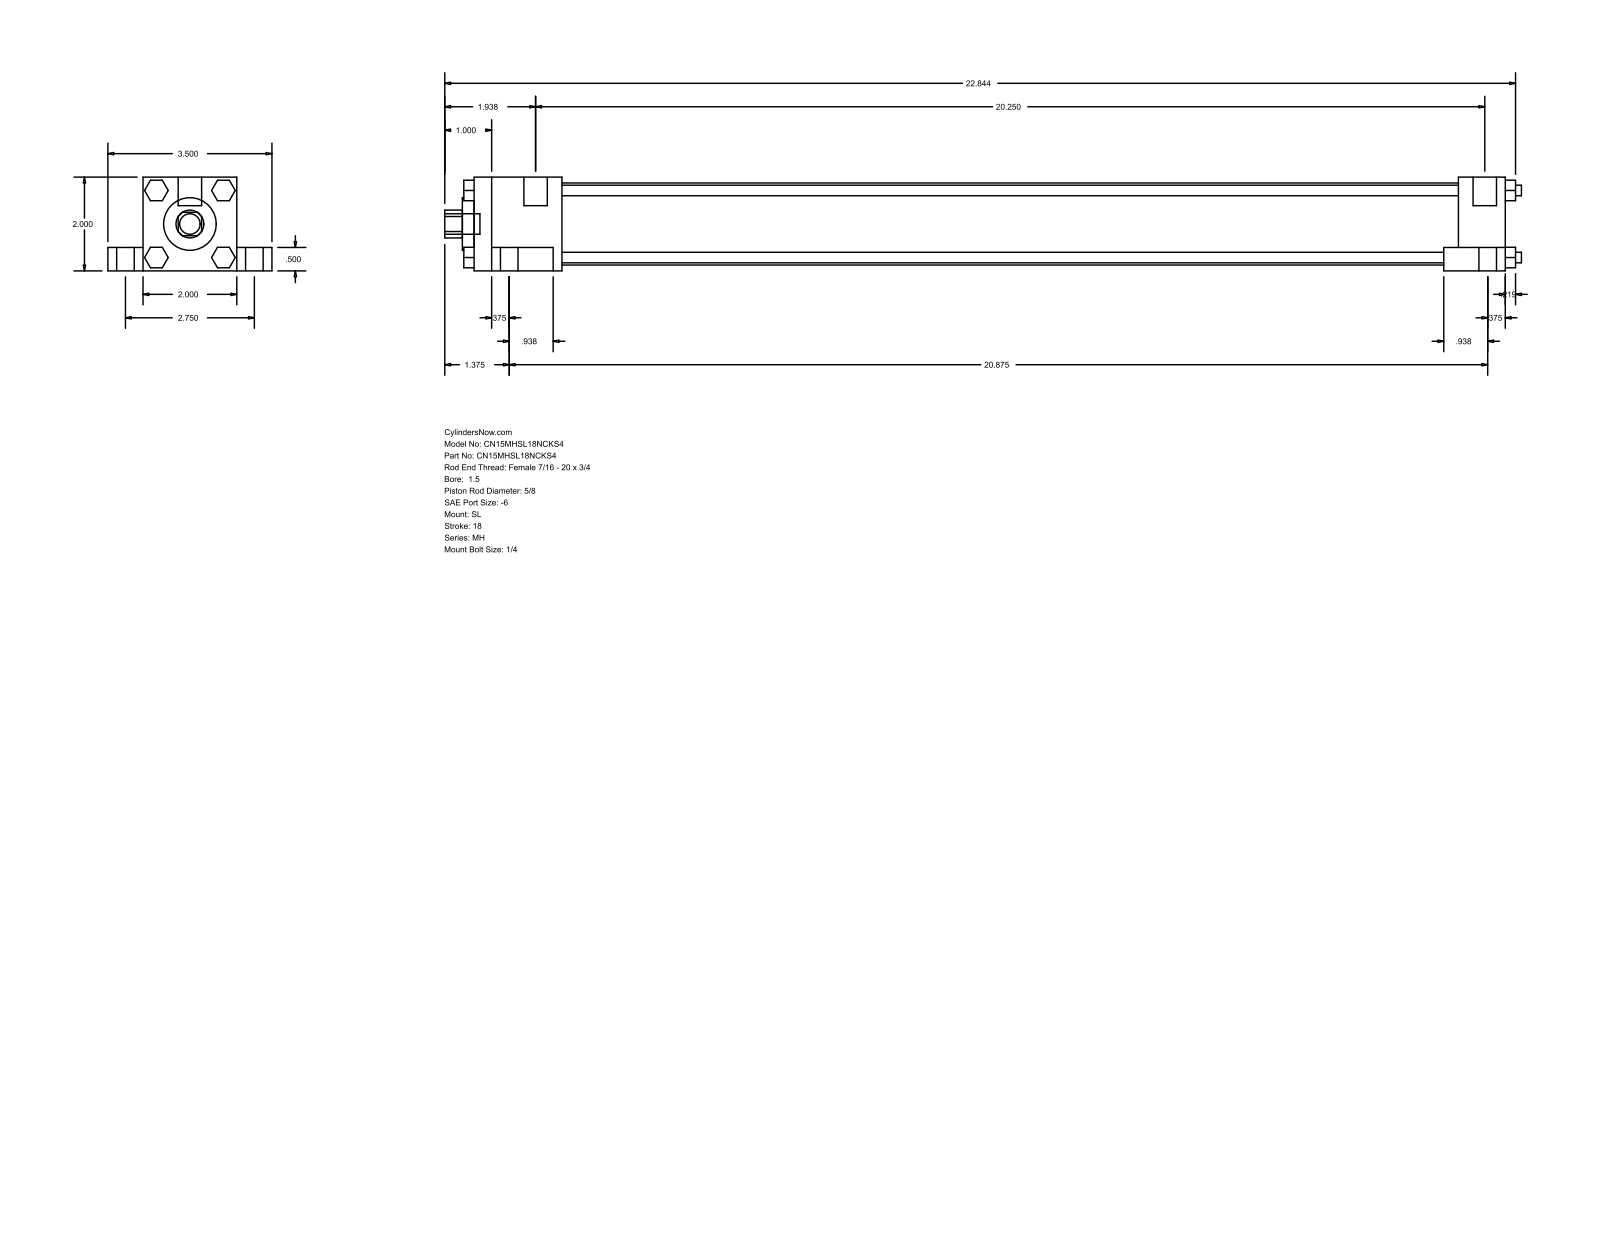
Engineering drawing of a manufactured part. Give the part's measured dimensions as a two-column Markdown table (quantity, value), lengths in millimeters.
| quantity | value |
| --- | --- |
| part name | MH_SL__0150_0.625 |
| STEP written by | GSSL Pune (CONFIG_CONTROL_DESIGN) |
| units | millimeters |
| bodies | 0 solids, 148 faces (112 planar, 36 cylindrical, 0 other) |
| overall size | 583.41 × 88.9 × 50.8 |
| round holes (diameter × count) | 15.88 × 1, 28.57 × 1, 44.45 × 1 |
| round bosses / shafts (diameter × count) | 15.88 × 4, 9.53 × 4, 5.71 × 4, 5.56 × 4, 12.7 × 2, 11.11 × 1 |
| partial cylindrical surfaces (radius × count) | 7.54 × 1 |
| main face-to-face distances | 50.8, 38.1, 19.05, 12.7, 69.85, 558.79, 9.52, 25.4, 533.39, 47.62 |
